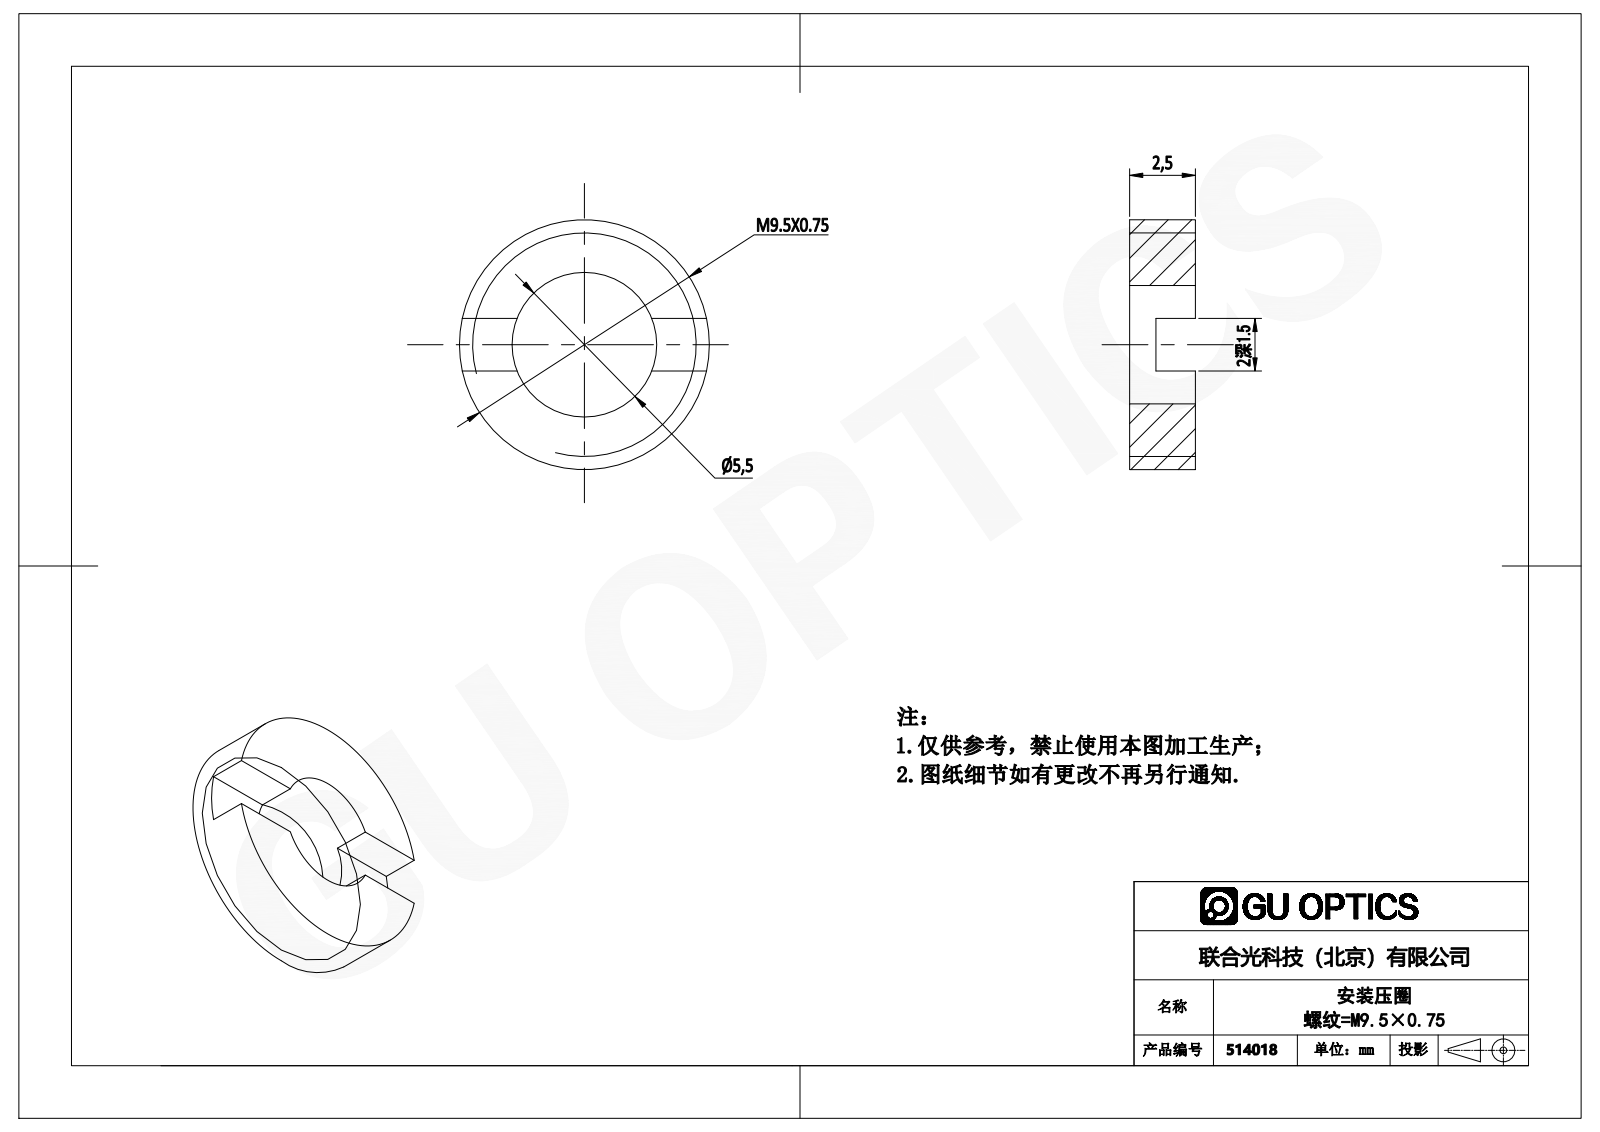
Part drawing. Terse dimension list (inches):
name: 514018
written by: SolidWorks 2016 (CONFIG_CONTROL_DESIGN)
unit: in
bodies: 1 solid, 13 faces (9 planar, 4 cylindrical, 0 other)
size: 0.374 × 0.374 × 0.098
volume: 0.006 in³; area: 0.329 in²
holes: 1× ⌀0.217
bosses: 1× ⌀0.374
face distances: 0.098, 0.039, 0.059, 0.079
